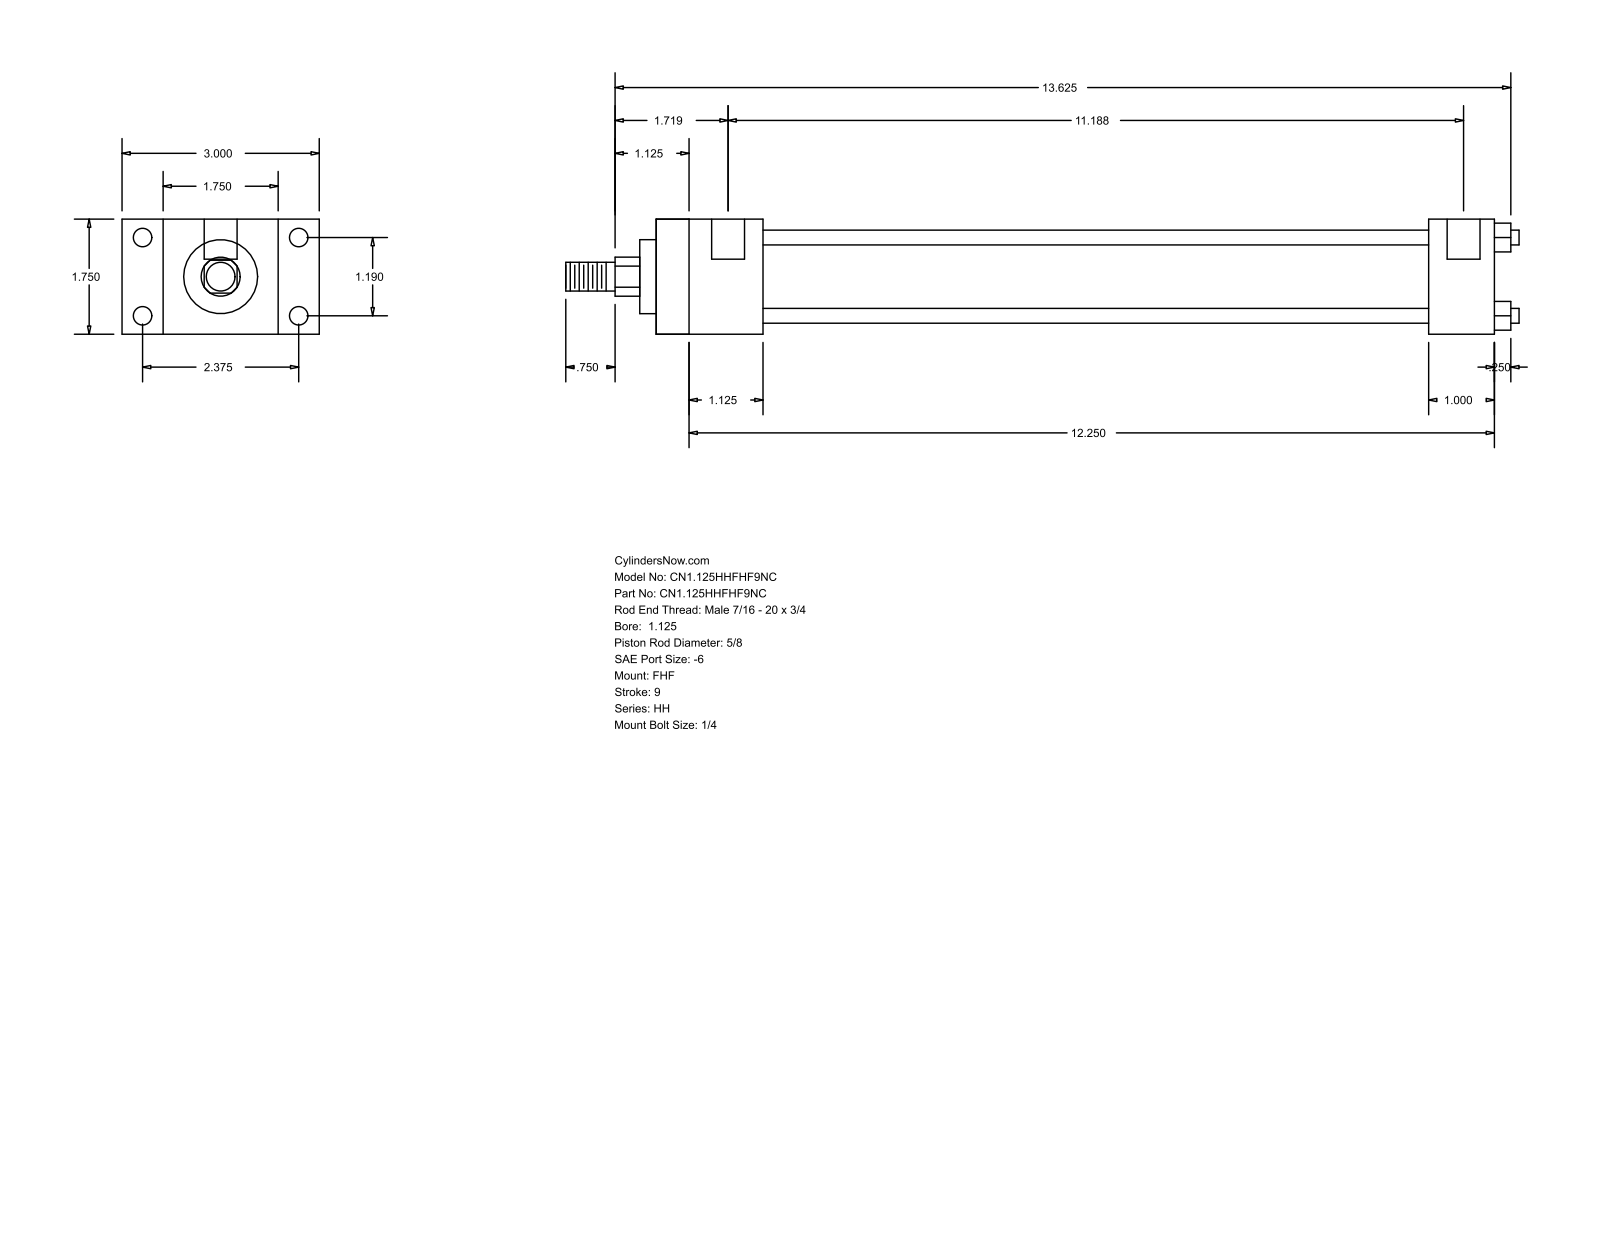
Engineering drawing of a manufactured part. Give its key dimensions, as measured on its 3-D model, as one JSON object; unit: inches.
{"part_name": "HH_FHF__0112_0.625", "step_written_by": "GSSL Pune (CONFIG_CONTROL_DESIGN)", "units": "inches", "bodies": {"solids": 0, "faces": 88, "planar": 60, "cylindrical": 28, "other": 0}, "overall_size": [14.5, 3, 1.75], "round_holes": [[0.219, 4], [0.281, 4], [0.5, 2]], "round_bosses_or_shafts": [[0.225, 4], [1.375, 1], [1.125, 1], [0.625, 1], [0.437, 1]], "partial_cylinders_radius": [[0.297, 1]], "face_to_face_distances": [1.75, 0.625, 2.375, 1.625, 3, 12.75, 11.125, 11.75, 10.125, 1], "hole_center_spacings": [1.19, 2.375, 2.656, 11.063, 0.125, 11.187]}
